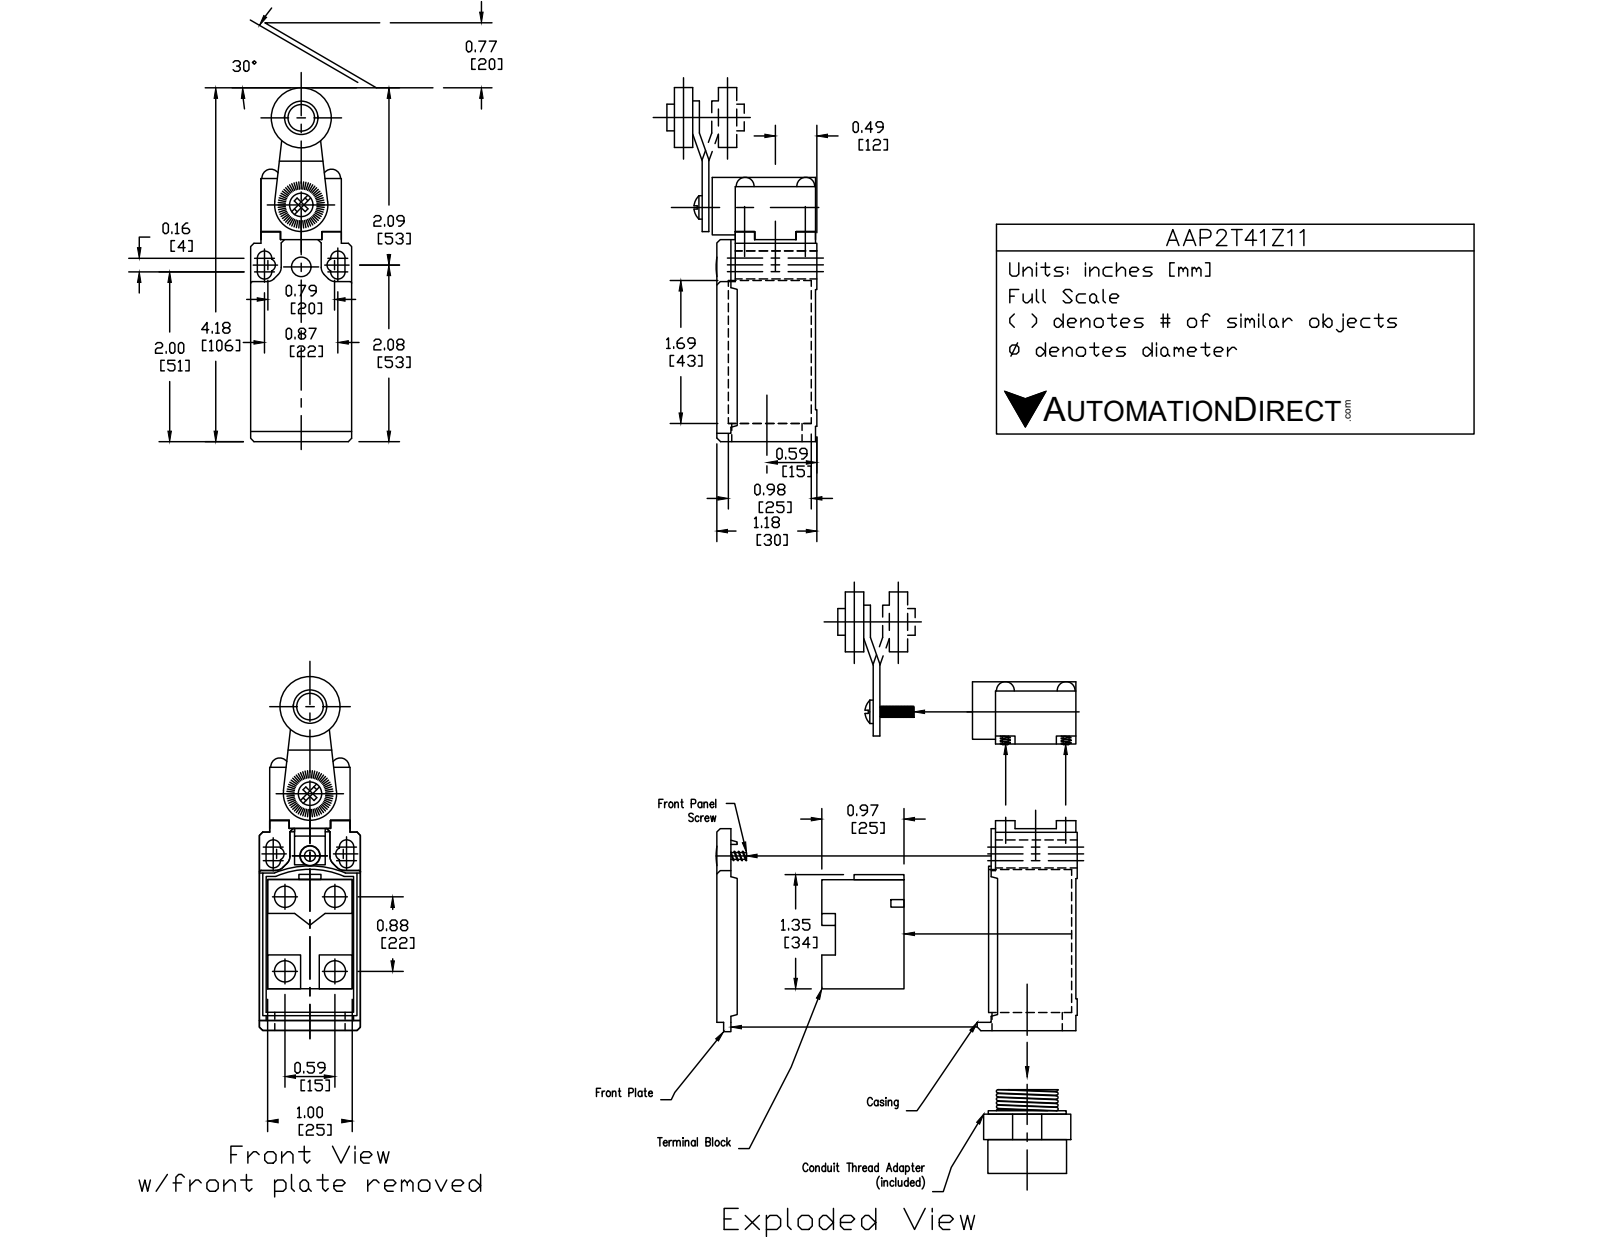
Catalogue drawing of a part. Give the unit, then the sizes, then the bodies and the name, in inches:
Units: inches
Overall size (bounding box): 4.193 × 1.717 × 1.193
Round holes (diameter × count): ⌀0.236 ×1, ⌀0.669 ×1, ⌀0.748 ×1
Round bosses / shafts (diameter × count): ⌀0.22 ×5, ⌀0.709 ×2, ⌀0.587 ×1, ⌀0.531 ×1, ⌀0.374 ×1, ⌀0.315 ×1, ⌀0.276 ×1, ⌀0.236 ×1
Partial cylindrical surfaces — rounded edges, fillets, slot ends (radius × count): R0.079 ×6, R0.118 ×6, R0.02 ×4, R0.039 ×2, R0.197 ×1, R0.315 ×1, R0.394 ×1, R0.4 ×1
Main face-to-face distances: 1.193, 1.165, 0.124, 1.069, 0.945, 0.236, 2.406, 1.181, 0.016, 0.276
Volume: 3.964 in³ · Surface area: 24.44 in²
Bodies: 3 solids, 214 faces (116 planar, 70 cylindrical, 28 other)
Part name (STEP PRODUCT): AAP2T41Z11
STEP written by: SolidWorks 2017 (AUTOMOTIVE_DESIGN)
